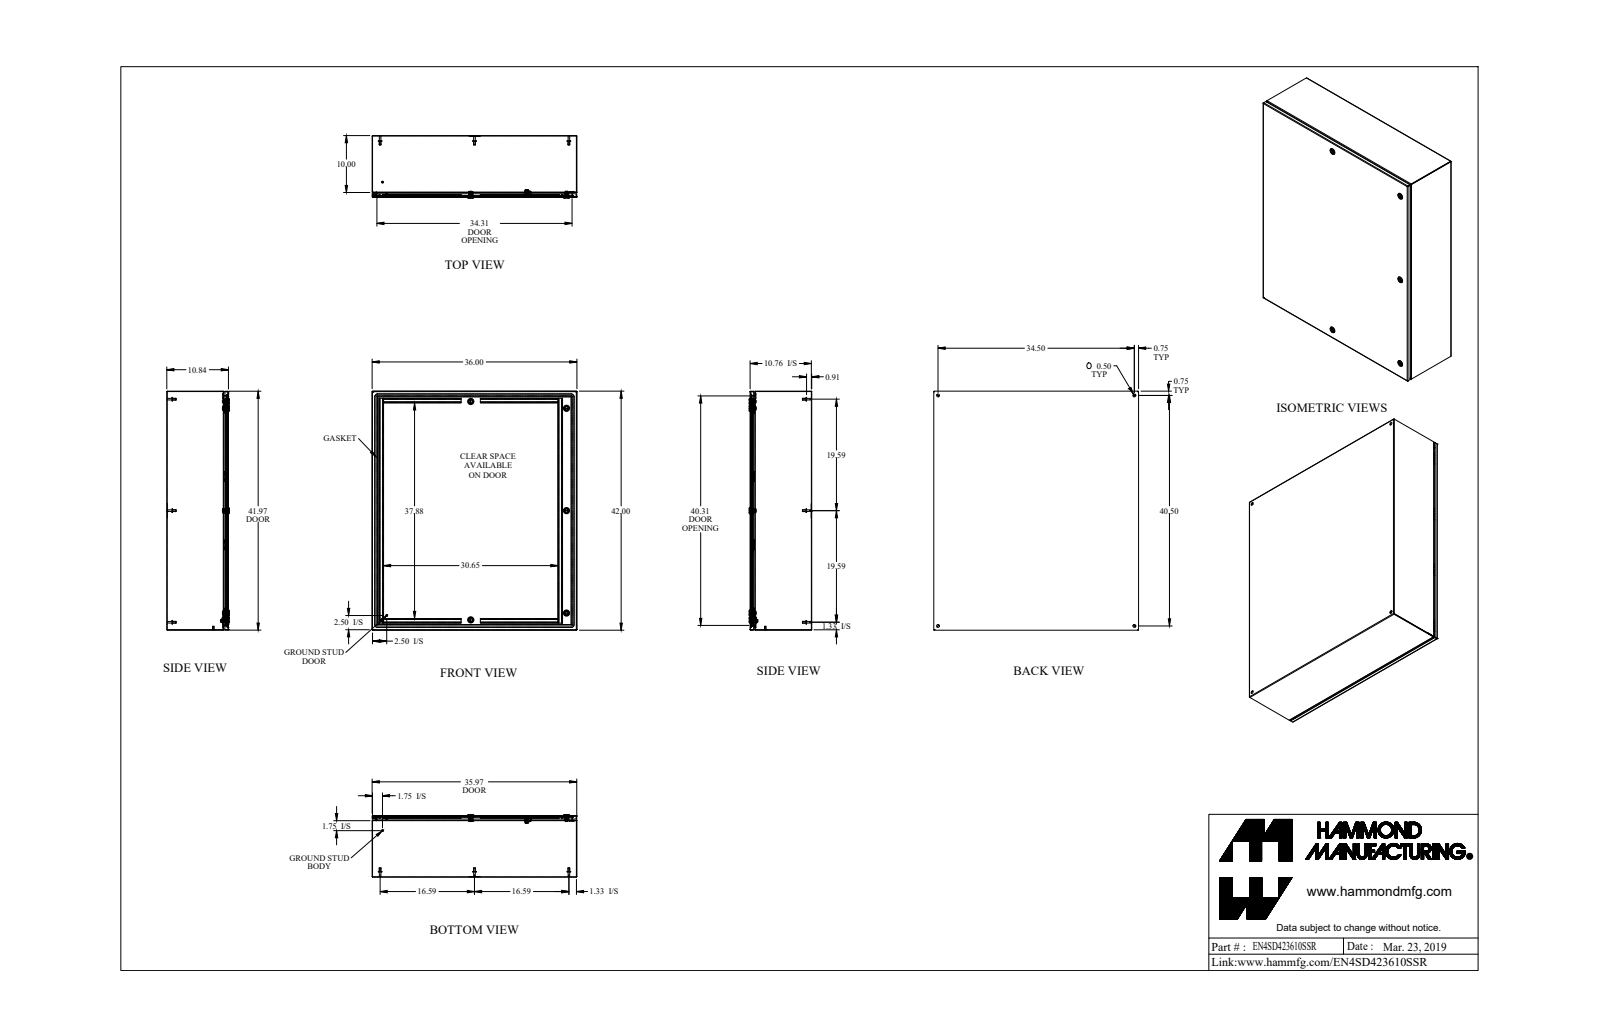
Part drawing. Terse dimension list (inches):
name: EN4SD423610SSR
written by: SolidWorks 2018 (AUTOMOTIVE_DESIGN)
unit: in
bodies: 64 solids, 1733 faces (896 planar, 552 cylindrical, 285 other)
size: 42 × 36 × 11.002
volume: 381.2 in³; area: 10 740 in²
holes: 9× ⌀0.5, 5× ⌀0.197, 5× ⌀0.387, 5× ⌀0.63, 5× ⌀0.768, 1× ⌀0.172, 1× ⌀0.196, 1× ⌀0.24, 1× ⌀0.242, 1× ⌀0.275, 1× ⌀0.375
bosses: 10× ⌀0.313, 9× ⌀0.625, 8× ⌀0.275, 5× ⌀1.1, 5× ⌀0.785, 5× ⌀0.625, 5× ⌀0.525, 5× ⌀0.236
rounds: 24× R0.01, 24× R0.048, 20× R0.036, 20× R0.108, 15× R0.062, 10× R0.094, 10× R0.125, 9× R0.016
face distances: 0.072, 10.77, 10.698, 10.842, 35.928, 41.928, 35.856, 36, 41.856, 42
hole spacings: 16.622, 16.881, 17.943, 20.278, 25.529, 33.504, 34.5, 39.082
